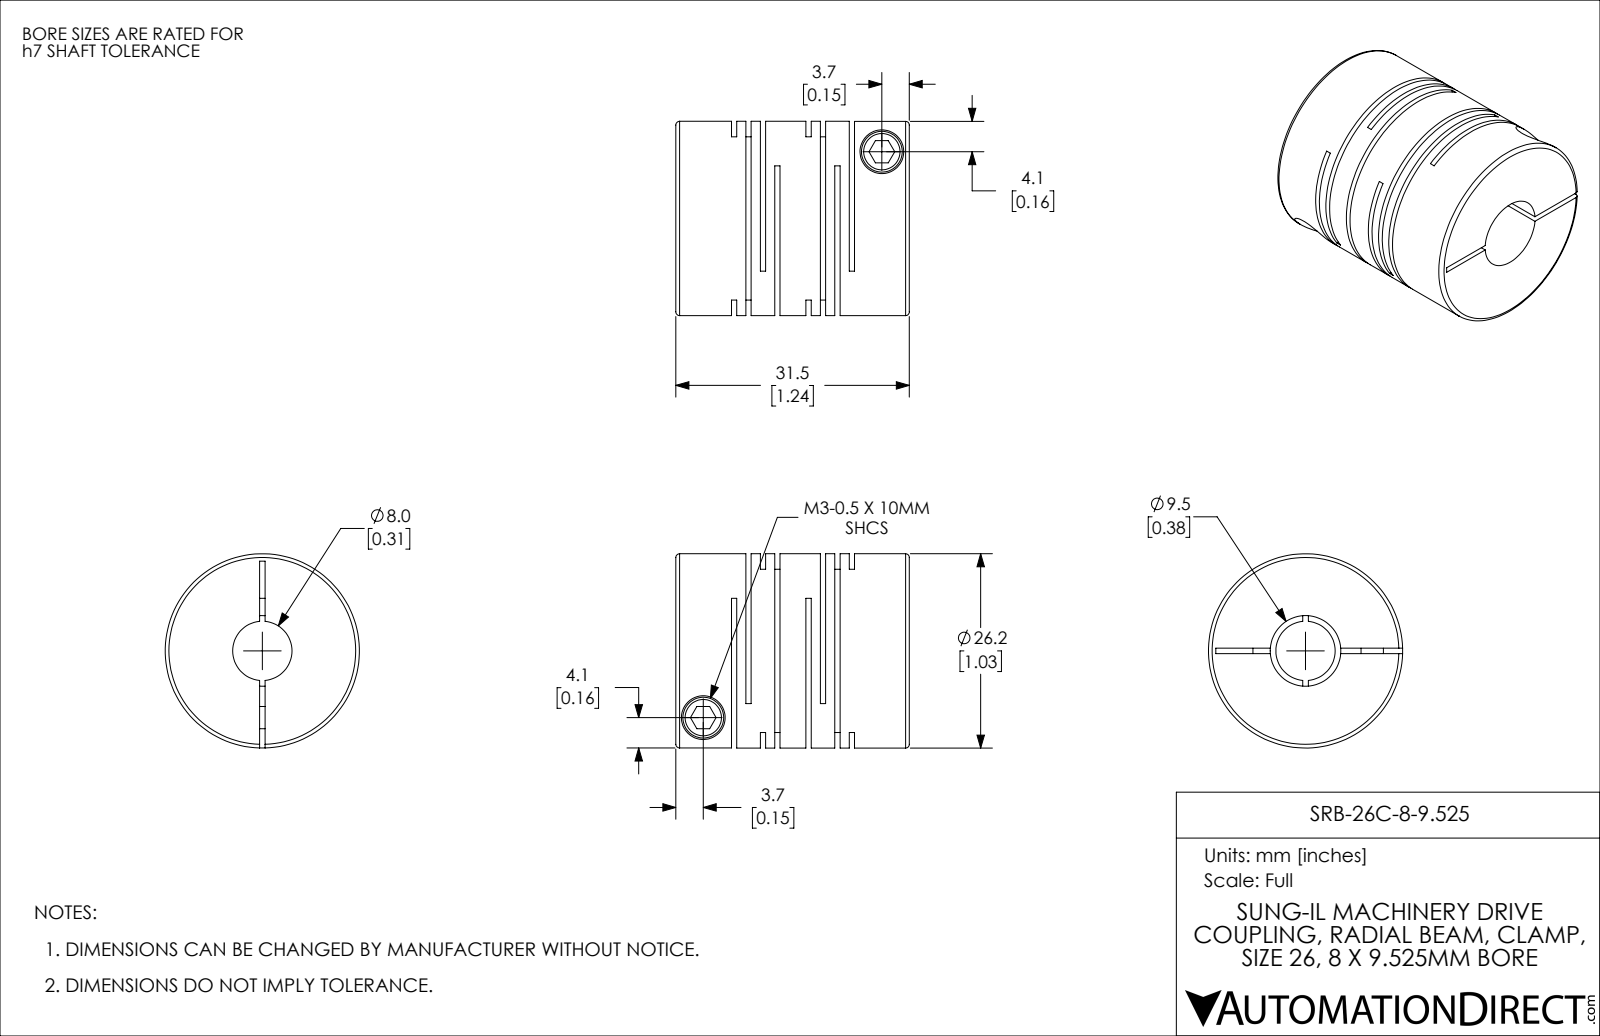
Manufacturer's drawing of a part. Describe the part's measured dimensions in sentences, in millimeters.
The part is named "SRB-26C-8-9.525". Its 3-D file was written by "SolidWorks 2021 (CONFIG_CONTROL_DESIGN)". It is 1 solid with 114 faces: 60 planar, 42 cylindrical and 12 other. Overall it measures 31.5 by 26.2 by 26.2 millimeters. Its volume is 12 275 cubic millimeters and its surface area 10 857 square millimeters. Round holes: 2 of diameter 3, 2 of diameter 5.9, 1 of diameter 8, 1 of diameter 9.53. Round bosses or shafts: 2 of diameter 5.5, 1 of diameter 26.2. The main face-to-face distances are 1.95, 10.05, 0.71, 3.9, 8.1, 12, 1.24, 2.66, 9.34, 13.95.
